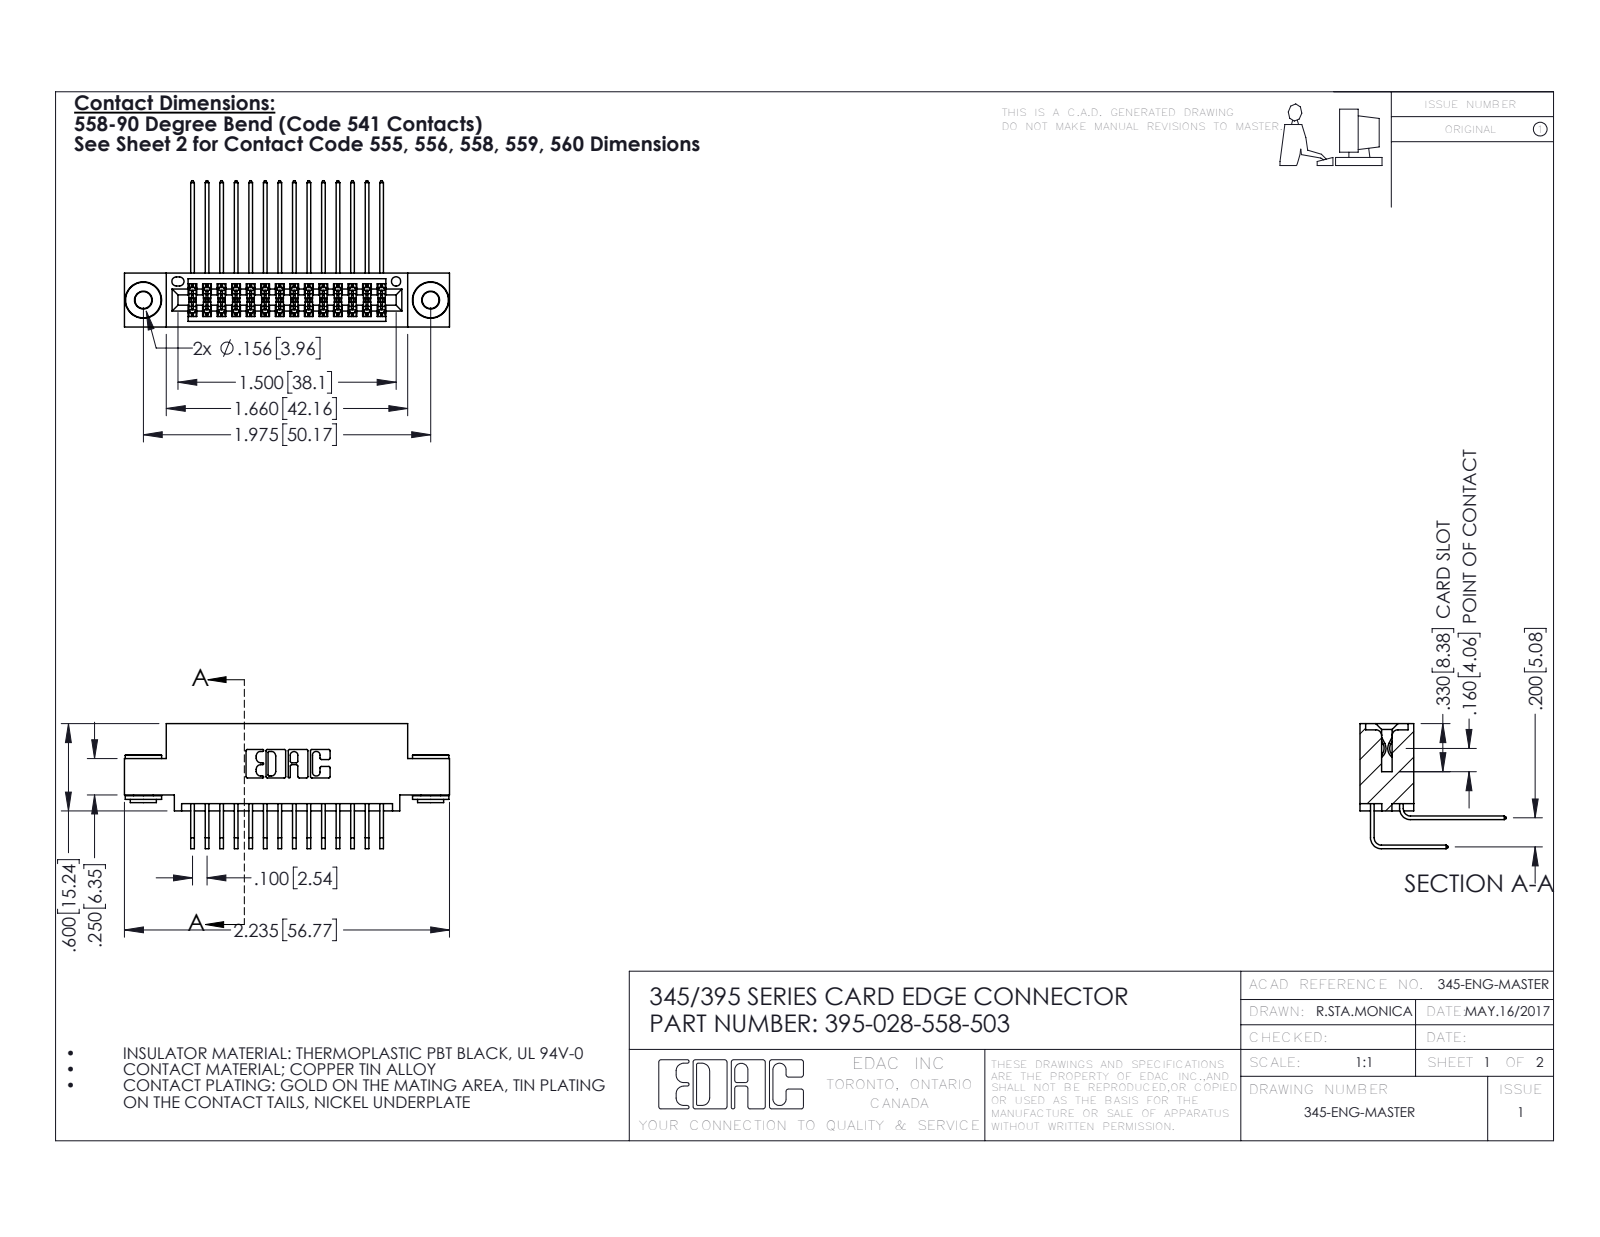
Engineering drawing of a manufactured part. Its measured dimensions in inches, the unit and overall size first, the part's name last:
Units: inches
Overall size (bounding box): 2.235 × 1.005 × 0.859
Round holes (diameter × count): ⌀0.116 ×2, ⌀0.156 ×2, ⌀0.064 ×1
Round bosses / shafts (diameter × count): ⌀0.25 ×2, ⌀0.18 ×2, ⌀0.136 ×2
Partial cylindrical surfaces — rounded edges, fillets, slot ends (radius × count): R0.006 ×43, R0.01 ×22, R0.007 ×6, R0.031 ×6, R0.026 ×3, R0.014 ×2, R0.019 ×2, R0.022 ×2
Main face-to-face distances: 0.2, 0.072, 0.298, 0.37, 0.025, 0.098, 0.272, 0.225, 0.1, 0.025
Hole centre spacings: 0.27, 1.742, 1.975
Volume: 0.327 in³ · Surface area: 13.08 in²
Bodies: 31 solids, 1624 faces (1074 planar, 542 cylindrical, 8 other)
Part name (STEP PRODUCT): 345-250-002_345-250-002-102; 345-292-001_558 Tail - 2; 395-028-558-503; 345 Part_0.110 Offset - 0.156 Dia-TH (+1 more)
STEP written by: SolidWorks 2016 (CONFIG_CONTROL_DESIGN)
